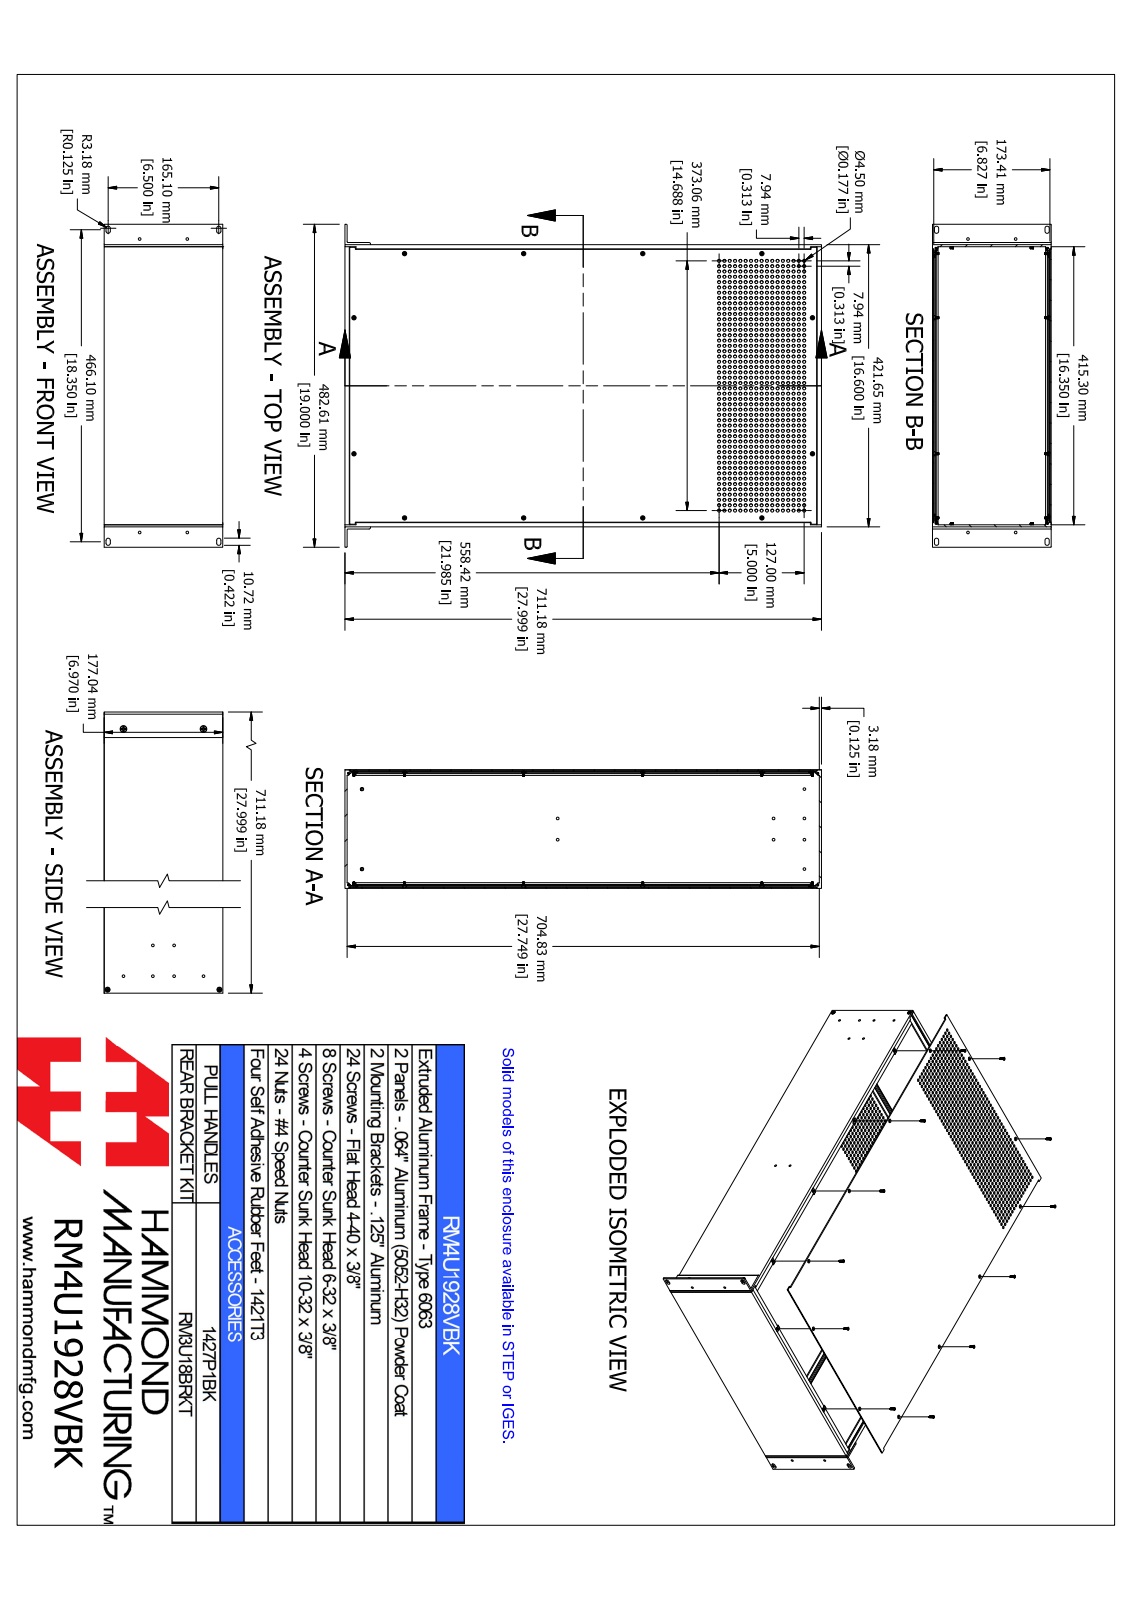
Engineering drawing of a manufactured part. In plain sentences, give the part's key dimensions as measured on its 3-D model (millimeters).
The part is named "RM4U1928VBK". Its 3-D file was written by "SolidWorks 2021 (AUTOMOTIVE_DESIGN)". It is 68 solids with 4268 faces: 1076 planar, 2260 cylindrical and 932 other. Overall it measures 711.2 by 482.6 by 177.1 millimeters. Its volume is 2 504 000 cubic millimeters and its surface area 2 150 000 square millimeters. Round holes: 1632 of diameter 4.5, 16 of diameter 4, 12 of diameter 4.1, 8 of diameter 4.2, 6 of diameter 4, 4 of diameter 4, 4 of diameter 4, 4 of diameter 4.3, 2 of diameter 5. Round bosses or shafts: 12 of diameter 5.1, 12 of diameter 2.8, 4 of diameter 6, 4 of diameter 3.5, 2 of diameter 9.1, 2 of diameter 4.8. Partial cylindrical surfaces (rounded edges, fillets, slot ends): 96 of radius 0.3, 96 of radius 0.6, 48 of radius 0.2, 48 of radius 0.4, 16 of radius 0.4, 16 of radius 1, 16 of radius 1, 11 of radius 0.9. The main face-to-face distances are 1.8, 175.2, 3.2, 177, 173.4, 418.5, 421.7, 415.3, 3.2, 711.2. The hole center spacings are 177.8, 433, 355.6, 531.4, 678.4, 122, 203.2, 270.8.
